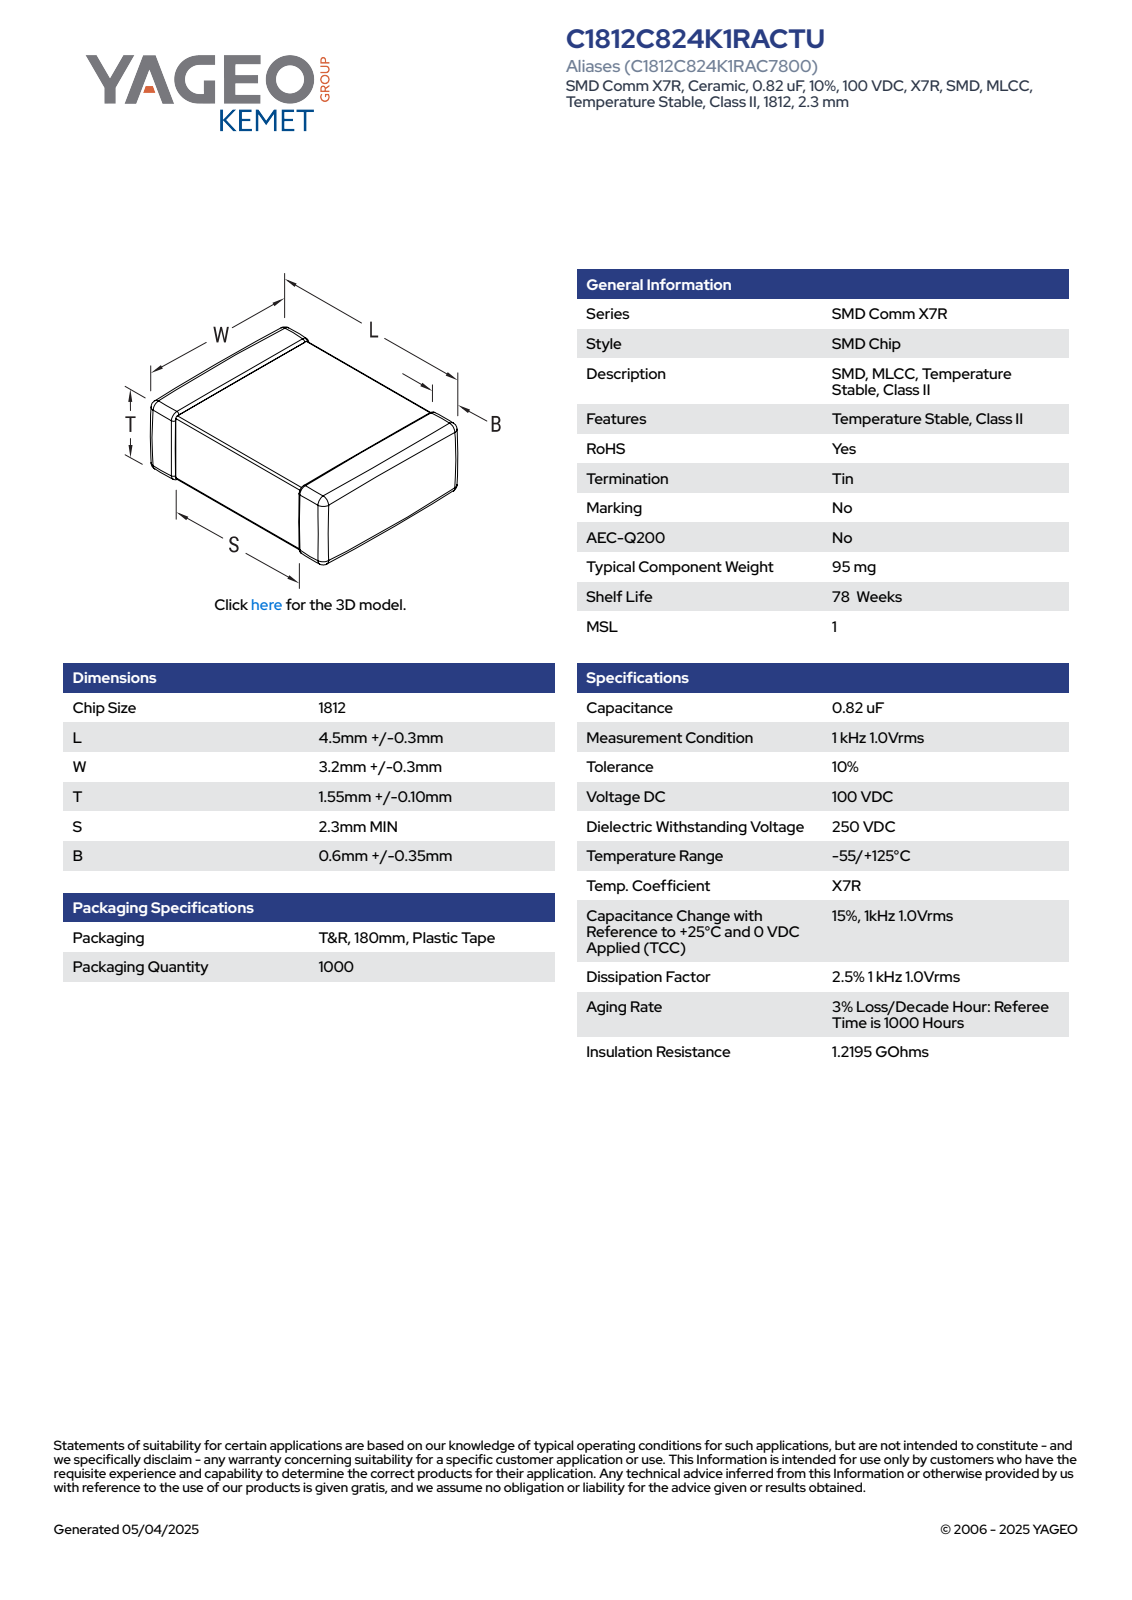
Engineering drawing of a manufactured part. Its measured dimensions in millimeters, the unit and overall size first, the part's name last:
Units: millimetres
Overall size (bounding box): 4.8 × 3.5 × 1.65
Main face-to-face distances: 1.58, 1.51, 1.65, 4.8, 3.43, 3.36, 3.5, 2.08, 2.72, 2.59
Volume: 26 mm³ · Surface area: 61 mm²
Bodies: 4 solids, 129 faces (71 planar, 42 cylindrical, 16 other)
Part name (STEP PRODUCT): CCS_CCSTD_1812_L4.8W3.5T1.65B0.6
STEP written by: SolidWorks 2021 (AUTOMOTIVE_DESIGN)
